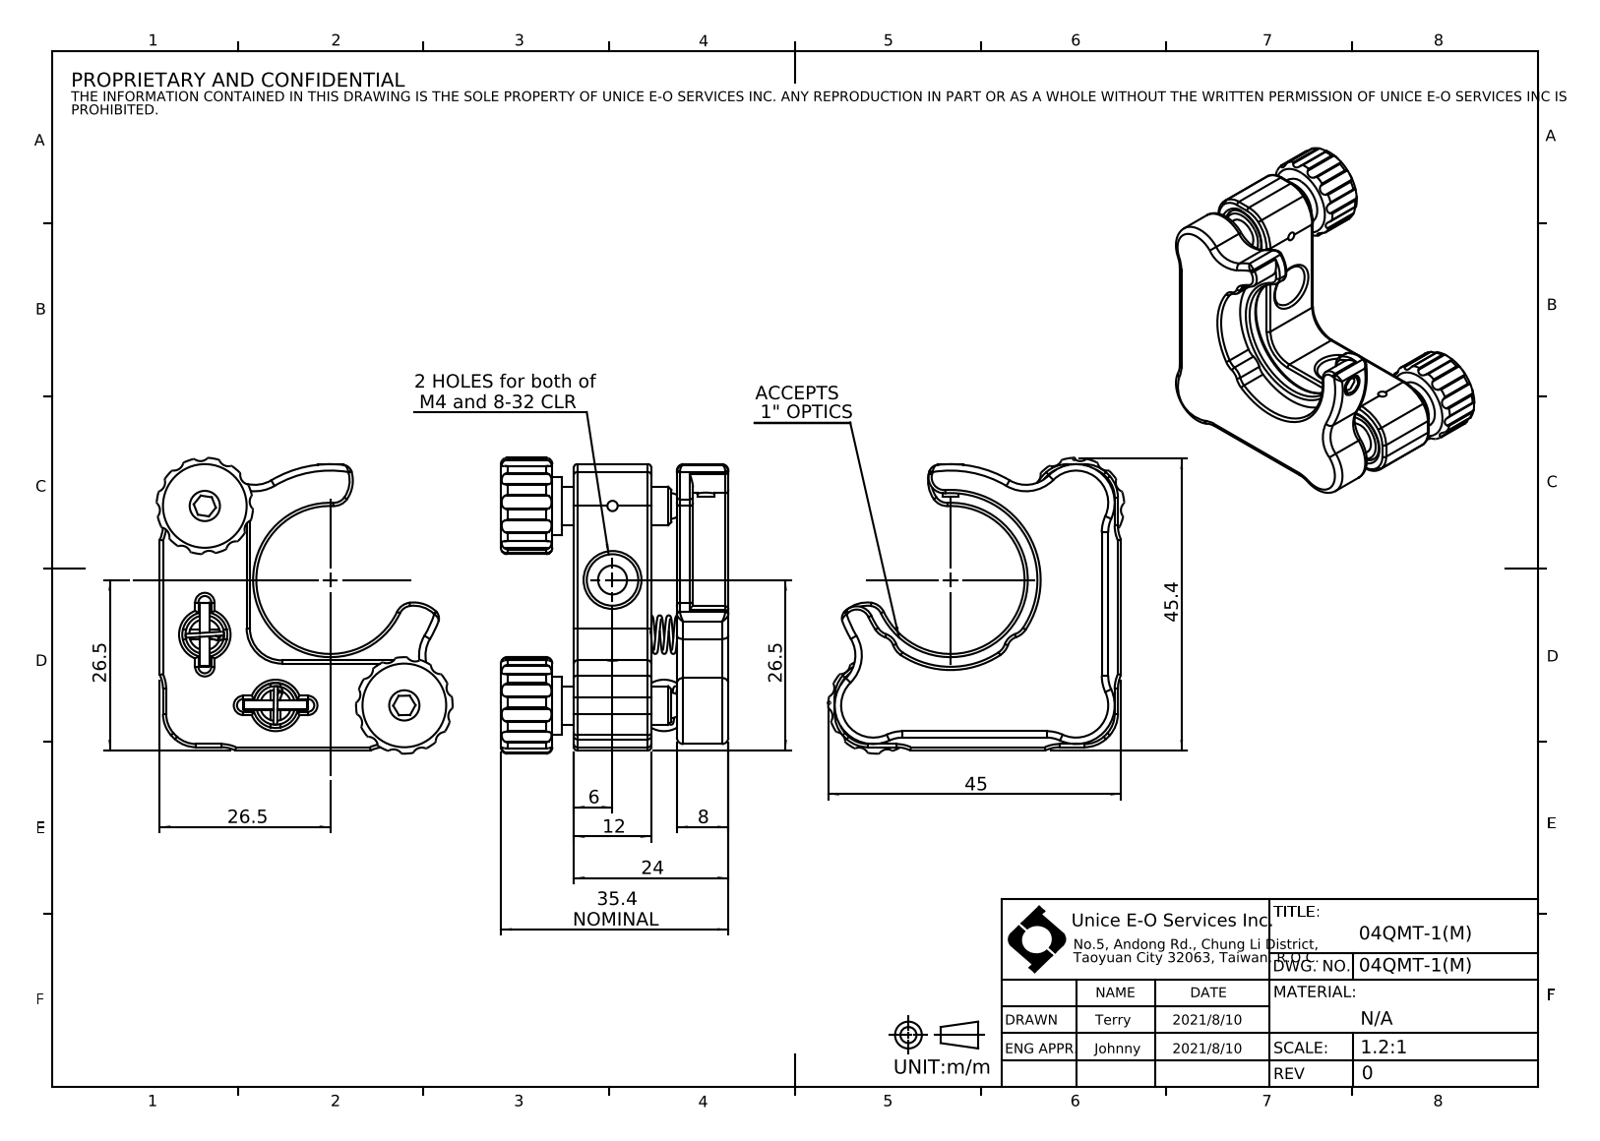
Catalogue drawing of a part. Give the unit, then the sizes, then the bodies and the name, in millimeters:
Units: millimetres
Overall size (bounding box): 45.98 × 45.98 × 35.35
Round holes (diameter × count): ⌀1 ×3, ⌀1.6 ×2, ⌀1.7 ×2, ⌀4.5 ×2, ⌀4.7 ×2, ⌀7 ×2, ⌀8 ×2, ⌀3.3 ×1, ⌀6 ×1
Round bosses / shafts (diameter × count): ⌀1.5 ×6, ⌀9 ×2, ⌀6 ×1, ⌀4 ×1, ⌀2.5 ×1
Partial cylindrical surfaces — rounded edges, fillets, slot ends (radius × count): R0.3 ×48, R1.5 ×27, R5 ×21, R0.5 ×20, R2.5 ×10, R1 ×8, R0.75 ×4, R6 ×3
Main face-to-face distances: 12, 8, 16, 4, 24, 27.35, 1.5, 14, 2, 11.35
Hole centre spacings: 11.5, 17.24, 20, 25, 32.89, 8.51, 14.5, 15.56
Bodies: 0 solids, 530 faces (72 planar, 273 cylindrical, 185 other)
Part name (STEP PRODUCT): 04QMT-1(M)
STEP written by: SolidWorks 2020 (CONFIG_CONTROL_DESIGN)
